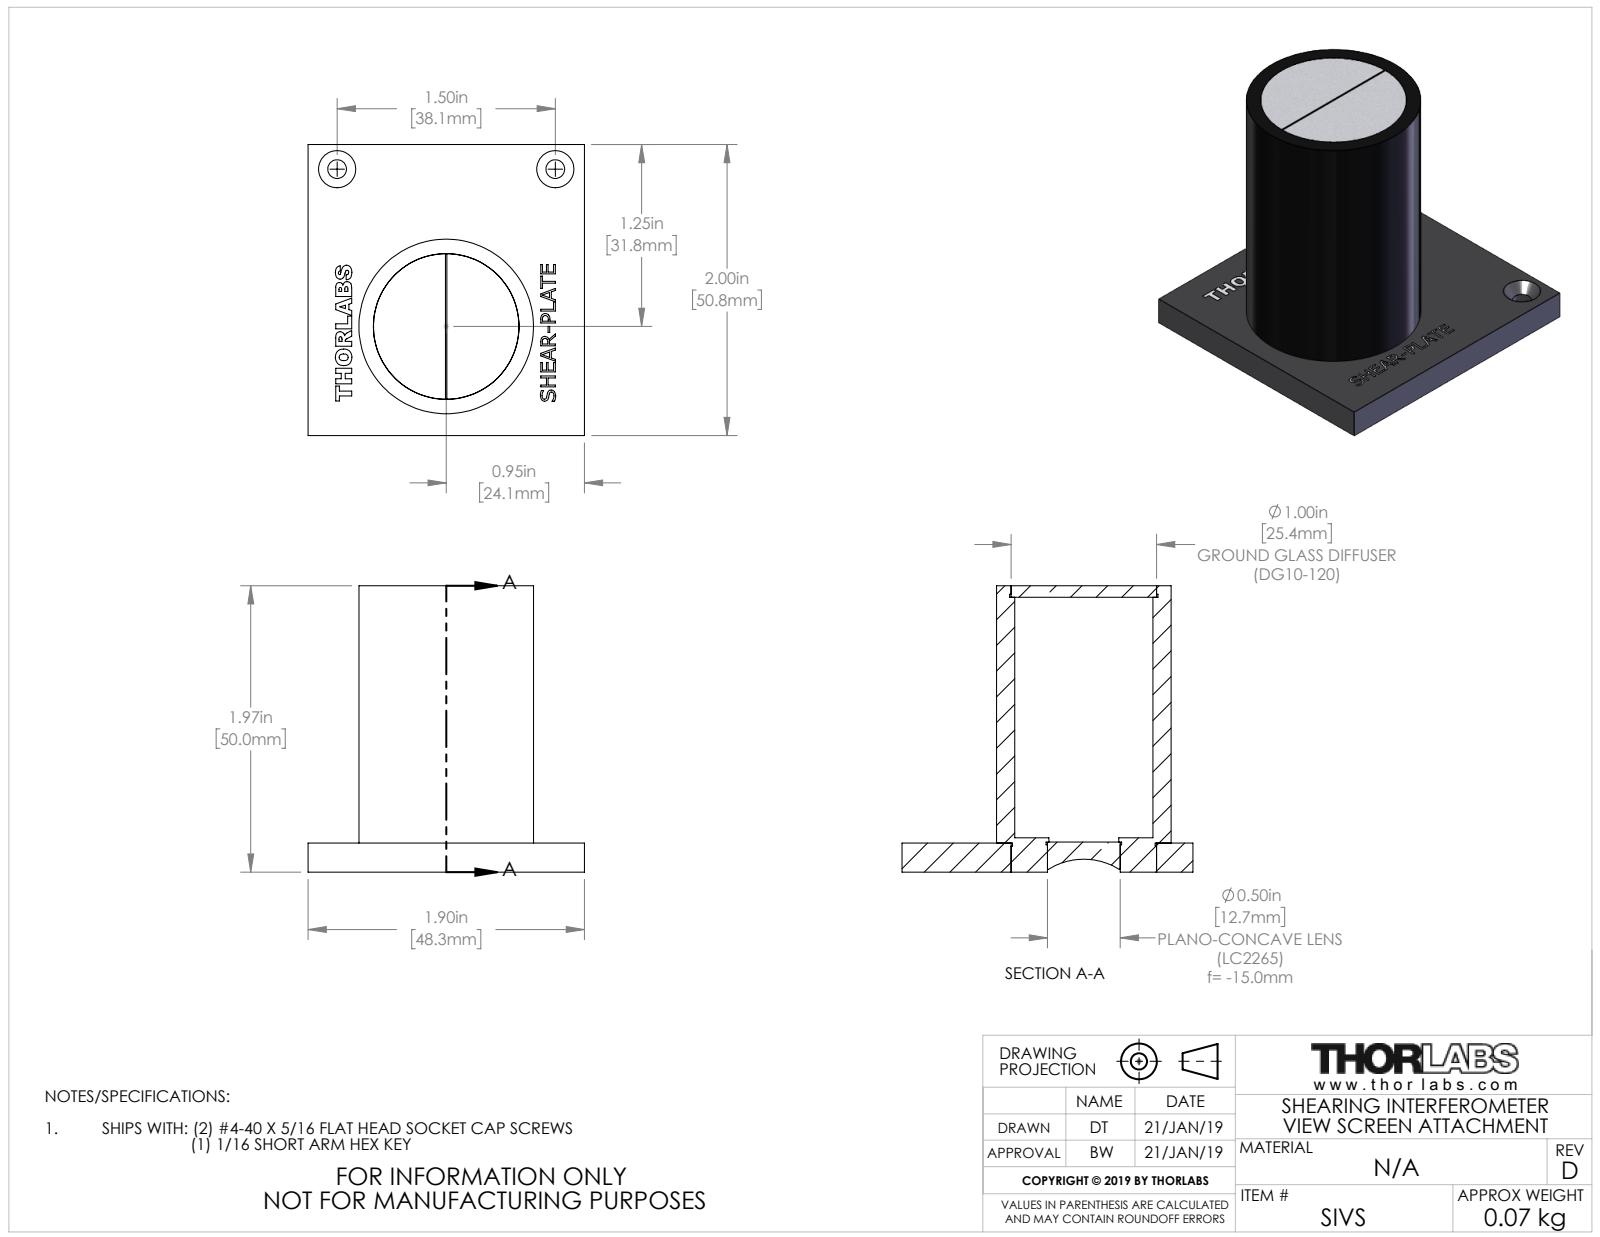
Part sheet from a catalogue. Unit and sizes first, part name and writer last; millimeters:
Units: millimetres
Overall size (bounding box): 50.8 × 50 × 48.3
Round holes (diameter × count): ⌀3.3 ×2, ⌀12.2 ×1, ⌀12.7 ×1, ⌀13.2 ×1, ⌀24.1 ×1, ⌀25.4 ×1, ⌀25.9 ×1
Round bosses / shafts (diameter × count): ⌀30.5 ×1, ⌀25.4 ×1, ⌀24.9 ×1, ⌀12.7 ×1
Main face-to-face distances: 5.1, 50, 44.9, 48, 42.9, 2, 6, 0.9, 42, 44
Hole centre spacings: 33.4, 38.1
Volume: 25 610 mm³ · Surface area: 16 590 mm²
Bodies: 4 solids, 88 faces (50 planar, 28 cylindrical, 10 other)
Part name (STEP PRODUCT): 16660-E0W
STEP written by: SolidWorks 2018 (CONFIG_CONTROL_DESIGN)
